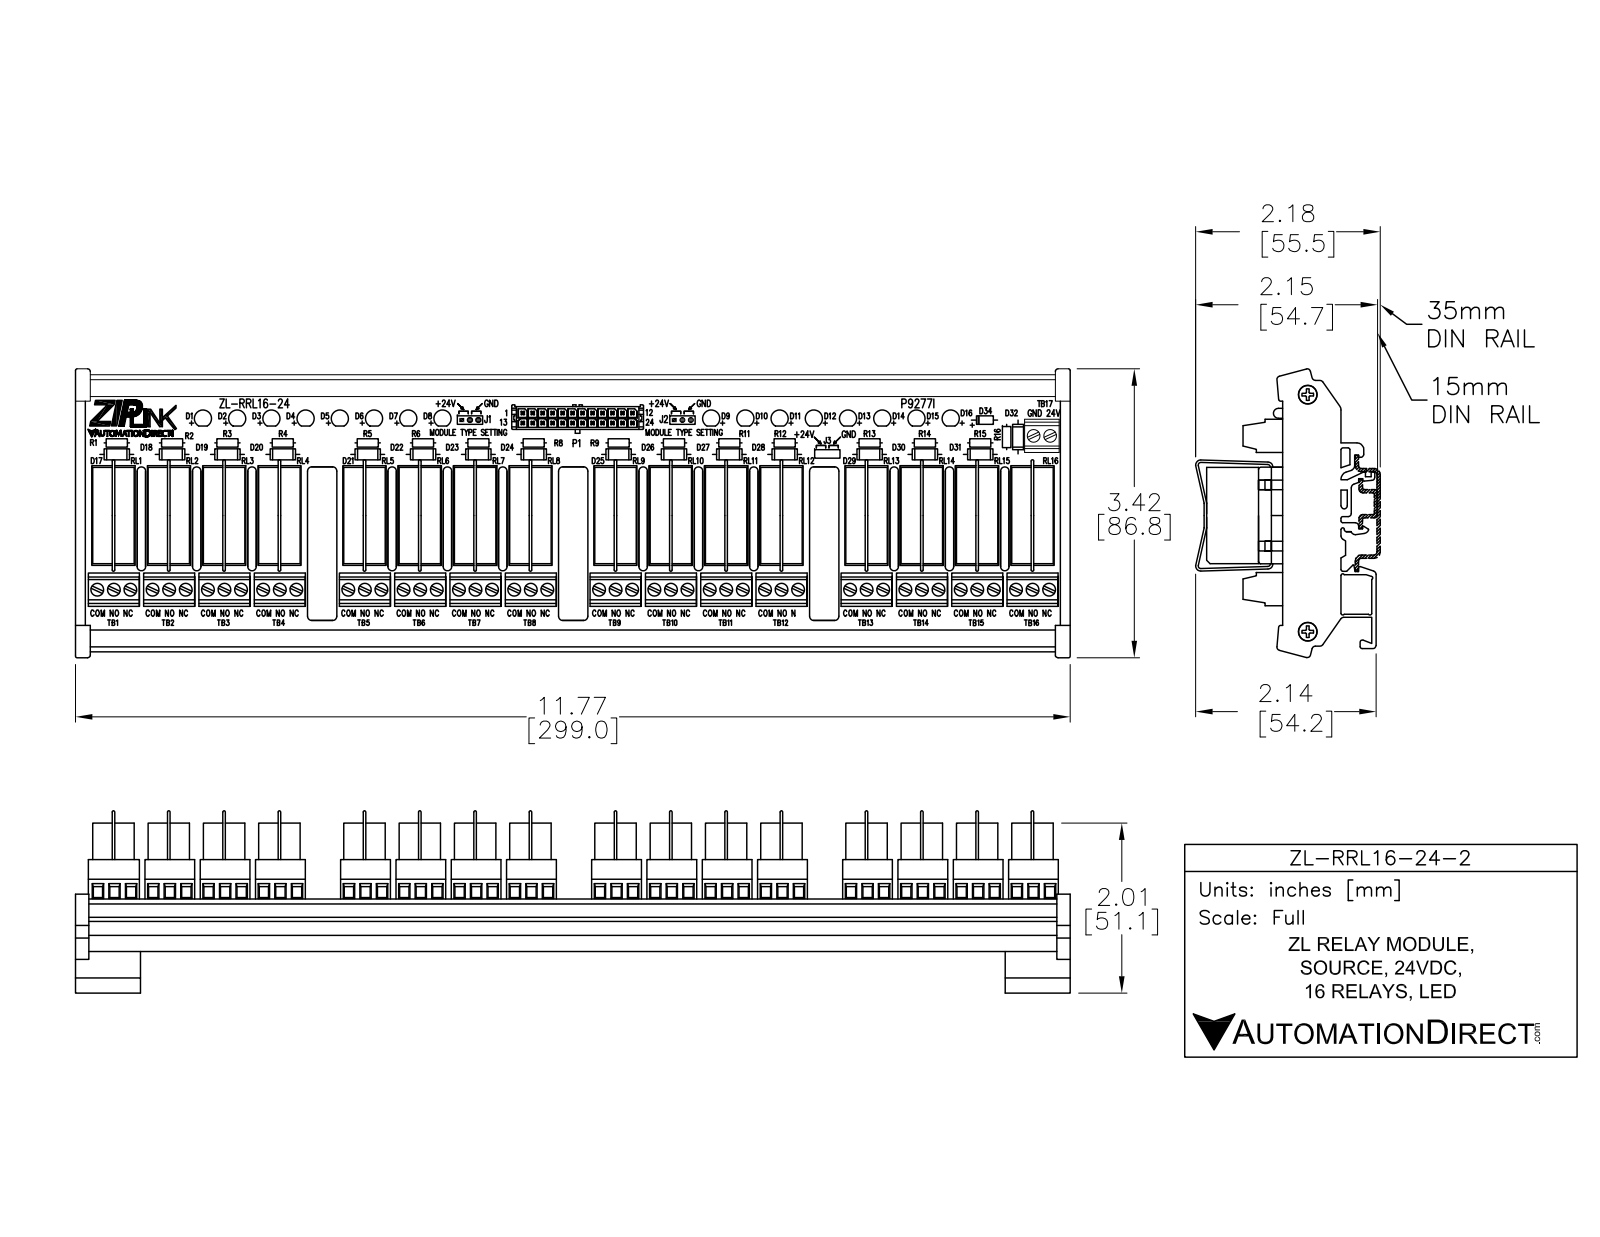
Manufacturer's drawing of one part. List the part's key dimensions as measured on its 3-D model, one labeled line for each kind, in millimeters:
Part name (STEP PRODUCT): ZL-RRL16-24-2
STEP written by: SolidWorks 2014 (AUTOMOTIVE_DESIGN)
Units: millimetres
Bodies: 21 solids, 2771 faces (1619 planar, 543 cylindrical, 609 other)
Overall size (bounding box): 300.2 × 86.9 × 55.5
Volume: 342 300 mm³ · Surface area: 181 000 mm²
Round holes (diameter × count): ⌀3.8 ×50, ⌀5.7 ×3
Round bosses / shafts (diameter × count): ⌀2 ×3, ⌀4.8 ×2, ⌀2.5 ×2, ⌀5.2 ×1, ⌀5.1 ×1
Partial cylindrical surfaces — rounded edges, fillets, slot ends (radius × count): R0.5 ×69, R0.4 ×35, R0.8 ×12, R1.5 ×12
Main face-to-face distances: 11, 3.5, 14.5, 75.4, 1.4, 16, 12.5, 16.8, 92.2, 33.5
Hole centre spacings: 75.4, 11.8, 16.6, 4.9, 58.8, 21.5, 33.3, 38.2
